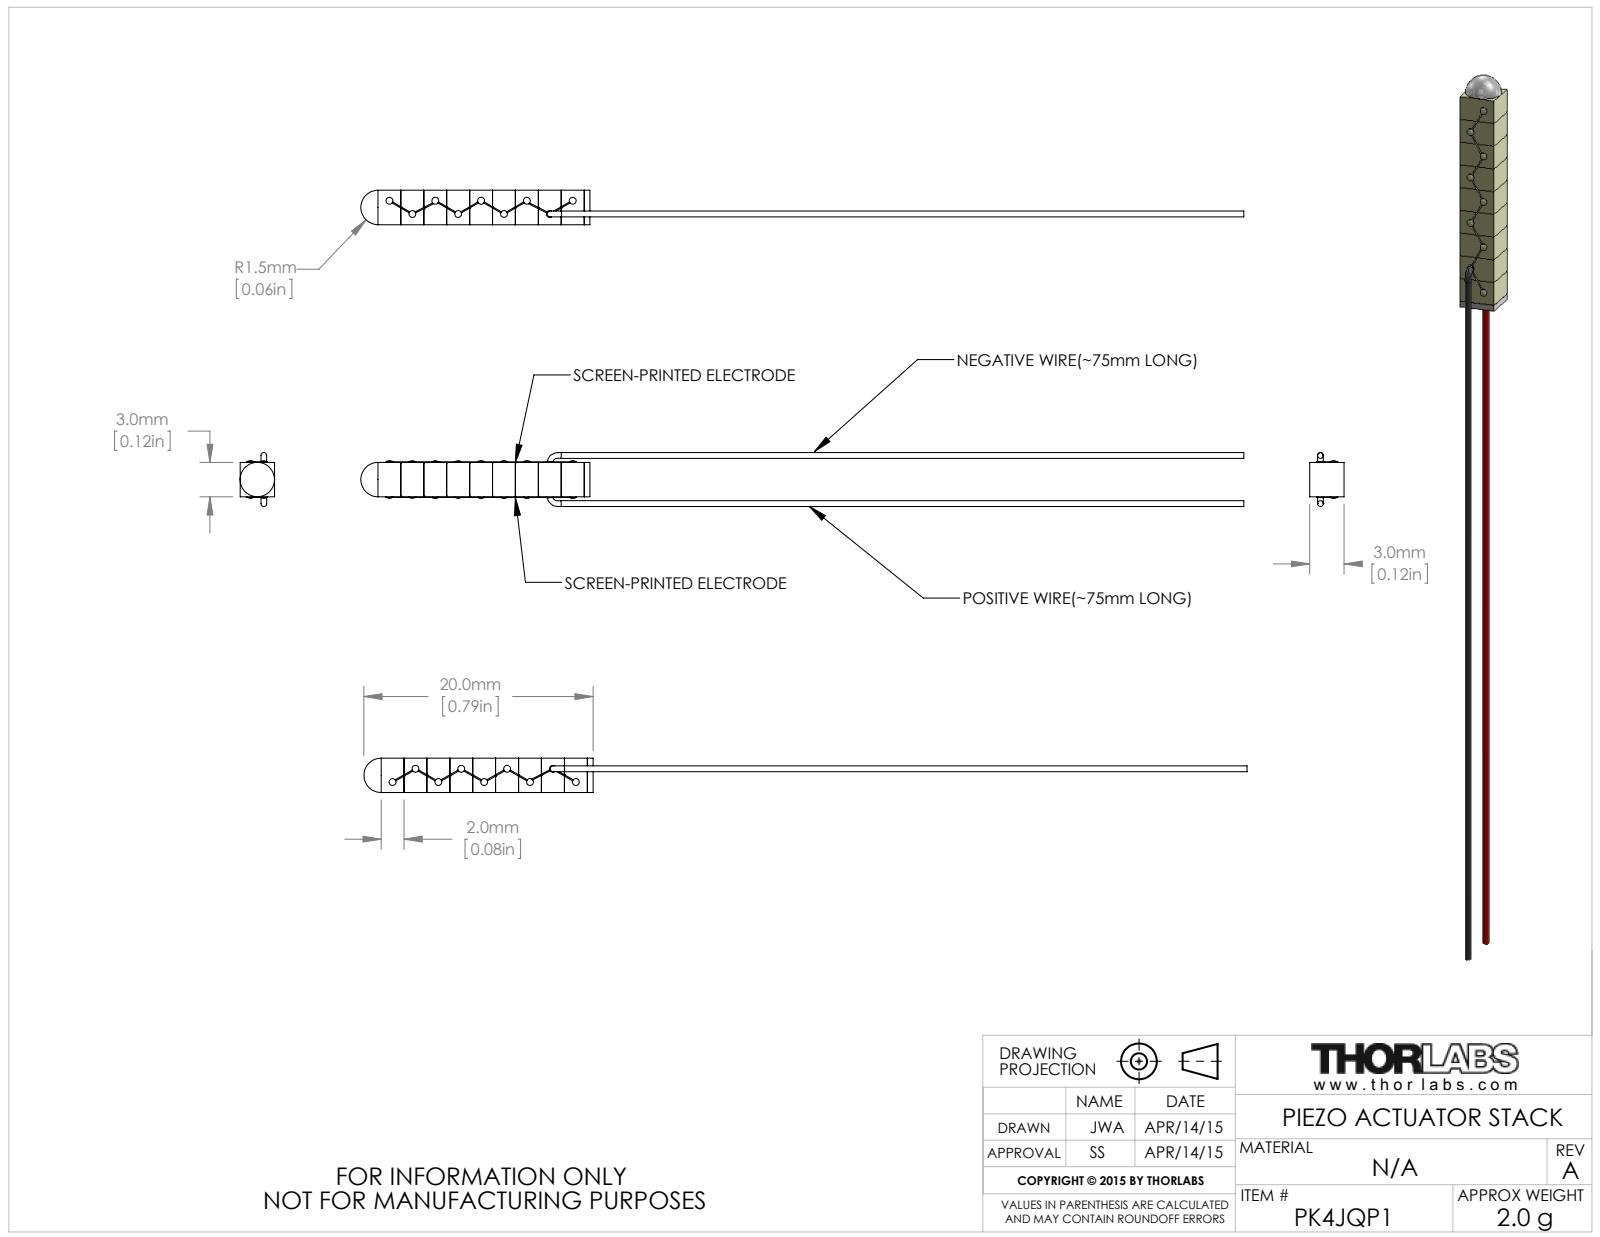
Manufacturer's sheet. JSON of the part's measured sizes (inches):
{"part_name": "CTN002957", "step_written_by": "SolidWorks 2014 (AUTOMOTIVE_DESIGN)", "units": "inches", "bodies": {"solids": 2, "faces": 202, "planar": 79, "cylindrical": 83, "other": 40}, "overall_size": [3.035, 0.186, 0.118], "volume_in3": 0.012, "surface_area_in2": 0.938, "round_bosses_or_shafts": [[0.024, 9]], "face_to_face_distances": [0.079, 0.157, 0.118, 0.236, 0.315, 0.394, 0.472, 0.551, 0.63, 0.02]}
